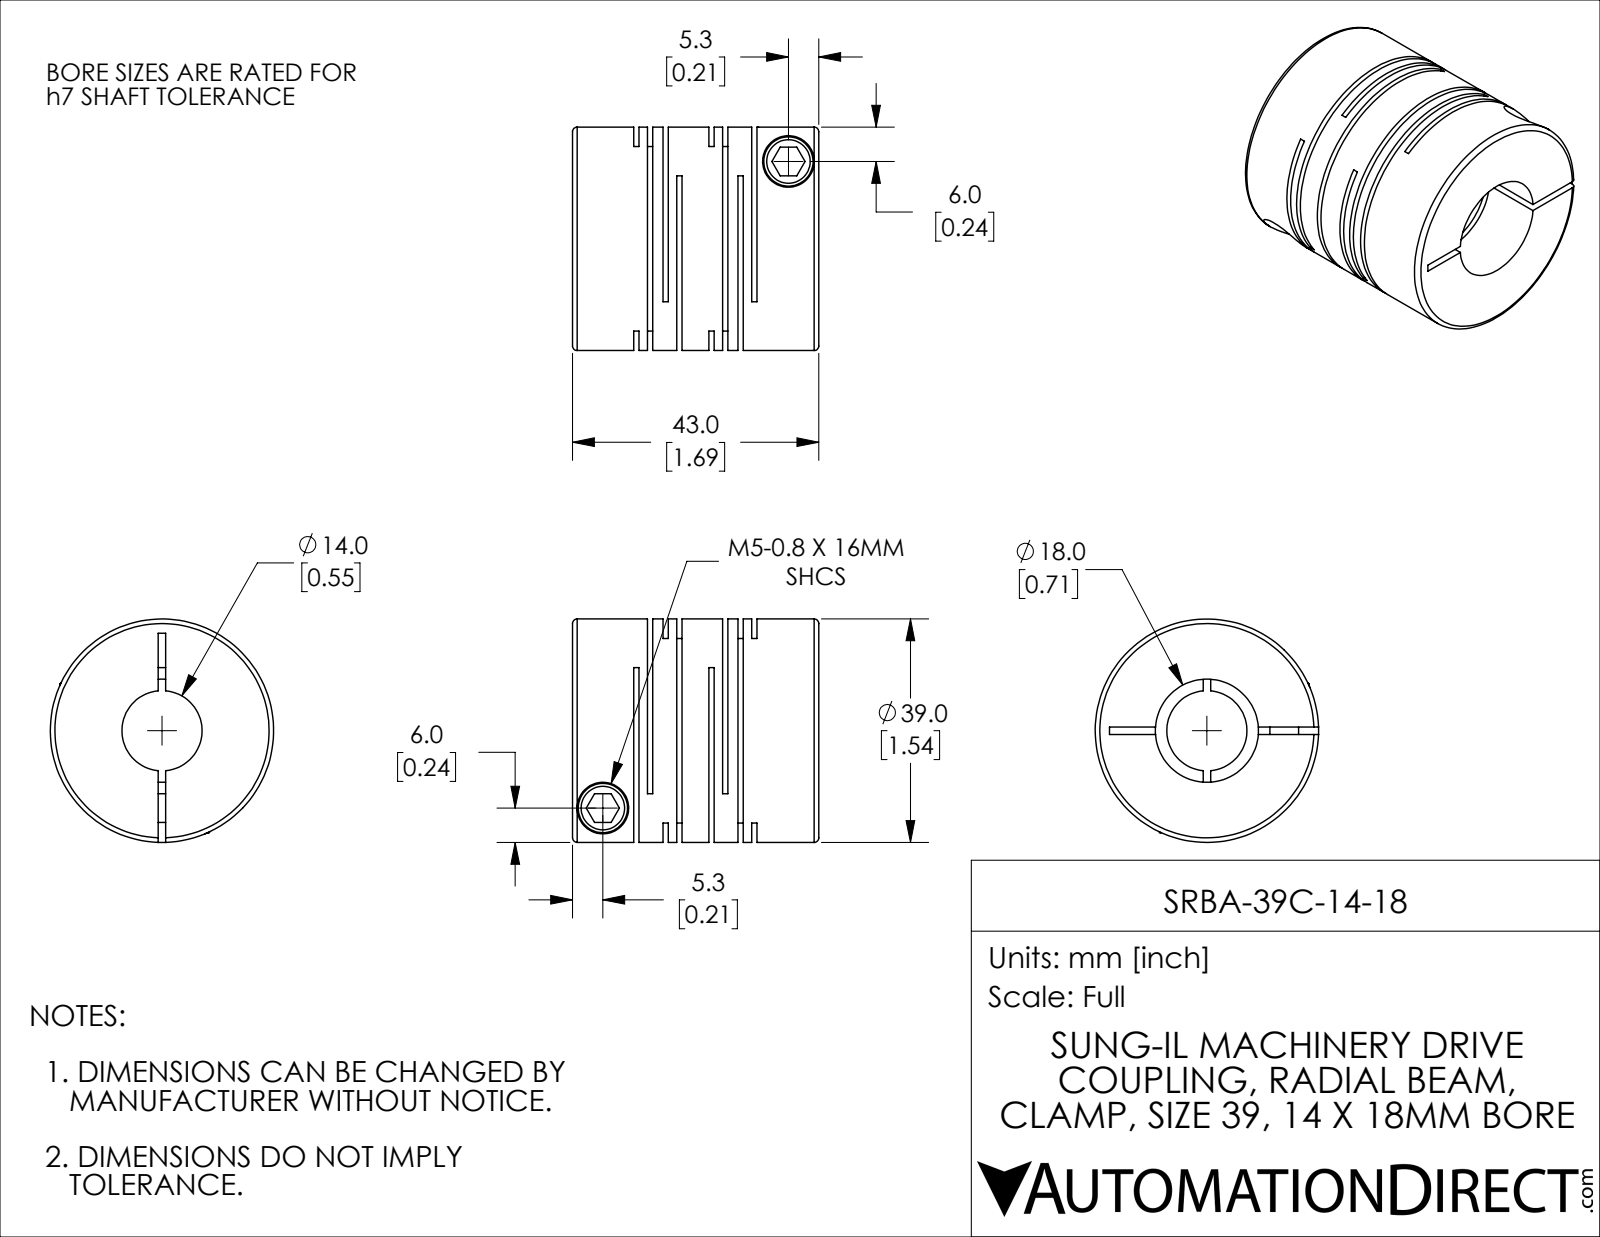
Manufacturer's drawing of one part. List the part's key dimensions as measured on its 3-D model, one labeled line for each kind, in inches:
Part name (STEP PRODUCT): SRBA-39C-14-18
STEP written by: SolidWorks 2021 (CONFIG_CONTROL_DESIGN)
Units: inches
Bodies: 1 solid, 114 faces (60 planar, 42 cylindrical, 12 other)
Overall size (bounding box): 1.693 × 1.535 × 1.535
Volume: 2.106 in³ · Surface area: 34.52 in²
Round holes (diameter × count): ⌀0.197 ×2, ⌀0.354 ×2, ⌀0.551 ×1, ⌀0.709 ×1
Round bosses / shafts (diameter × count): ⌀0.339 ×2, ⌀1.535 ×1
Main face-to-face distances: 0.516, 0.036, 0.094, 0.201, 0.421, 0.552, 0.717, 0.131, 0.058, 0.61
